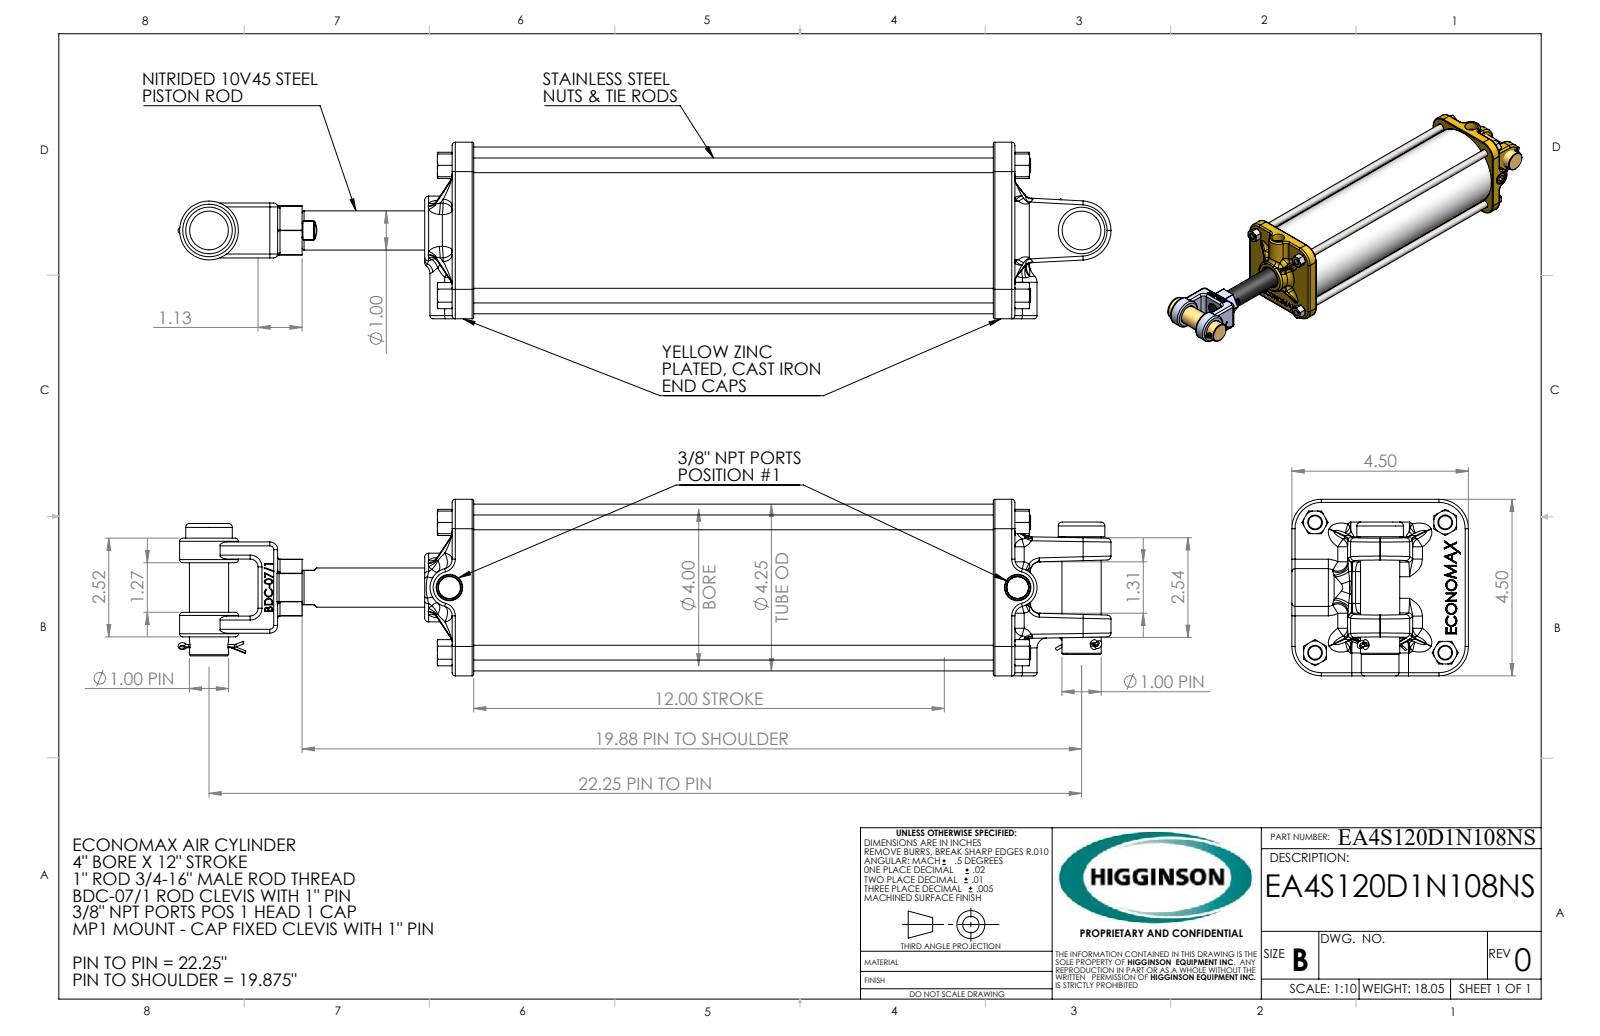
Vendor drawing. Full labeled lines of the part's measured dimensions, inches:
Part name (STEP PRODUCT): APT40-0.75-16; 1R10S063-18M4; CLPY-1000-3000; BDC-07-1 (+8 more)
STEP written by: SolidWorks 2021 (CONFIG_CONTROL_DESIGN)
Units: inches
Bodies: 23 solids, 1609 faces (388 planar, 254 cylindrical, 967 other)
Overall size (bounding box): 23.789 × 4.5 × 4.5
Volume: 92.33 in³ · Surface area: 748.8 in²
Round holes (diameter × count): ⌀0.254 ×2, ⌀0.562 ×2, ⌀0.687 ×1, ⌀0.75 ×1, ⌀0.754 ×1, ⌀0.785 ×1, ⌀1.002 ×1, ⌀1.05 ×1, ⌀1.128 ×1, ⌀1.14 ×1, ⌀1.142 ×1, ⌀1.371 ×1
Round bosses / shafts (diameter × count): ⌀0.375 ×4, ⌀1 ×3, ⌀1.188 ×2, ⌀4.25 ×1, ⌀3.992 ×1, ⌀3.985 ×1, ⌀3.74 ×1, ⌀3.634 ×1
Partial cylindrical surfaces — rounded edges, fillets, slot ends (radius × count): R0.1 ×24, R0.25 ×19, R0.039 ×8, R0.04 ×8, R0.08 ×8, R0.01 ×6, R0.02 ×6, R0.06 ×6
Main face-to-face distances: 0.55, 13.8, 13.25, 1.25, 14.35, 1.8, 12, 12.55, 1.24, 0.425
Hole centre spacings: 1.493, 1.63, 20.62, 22.25
